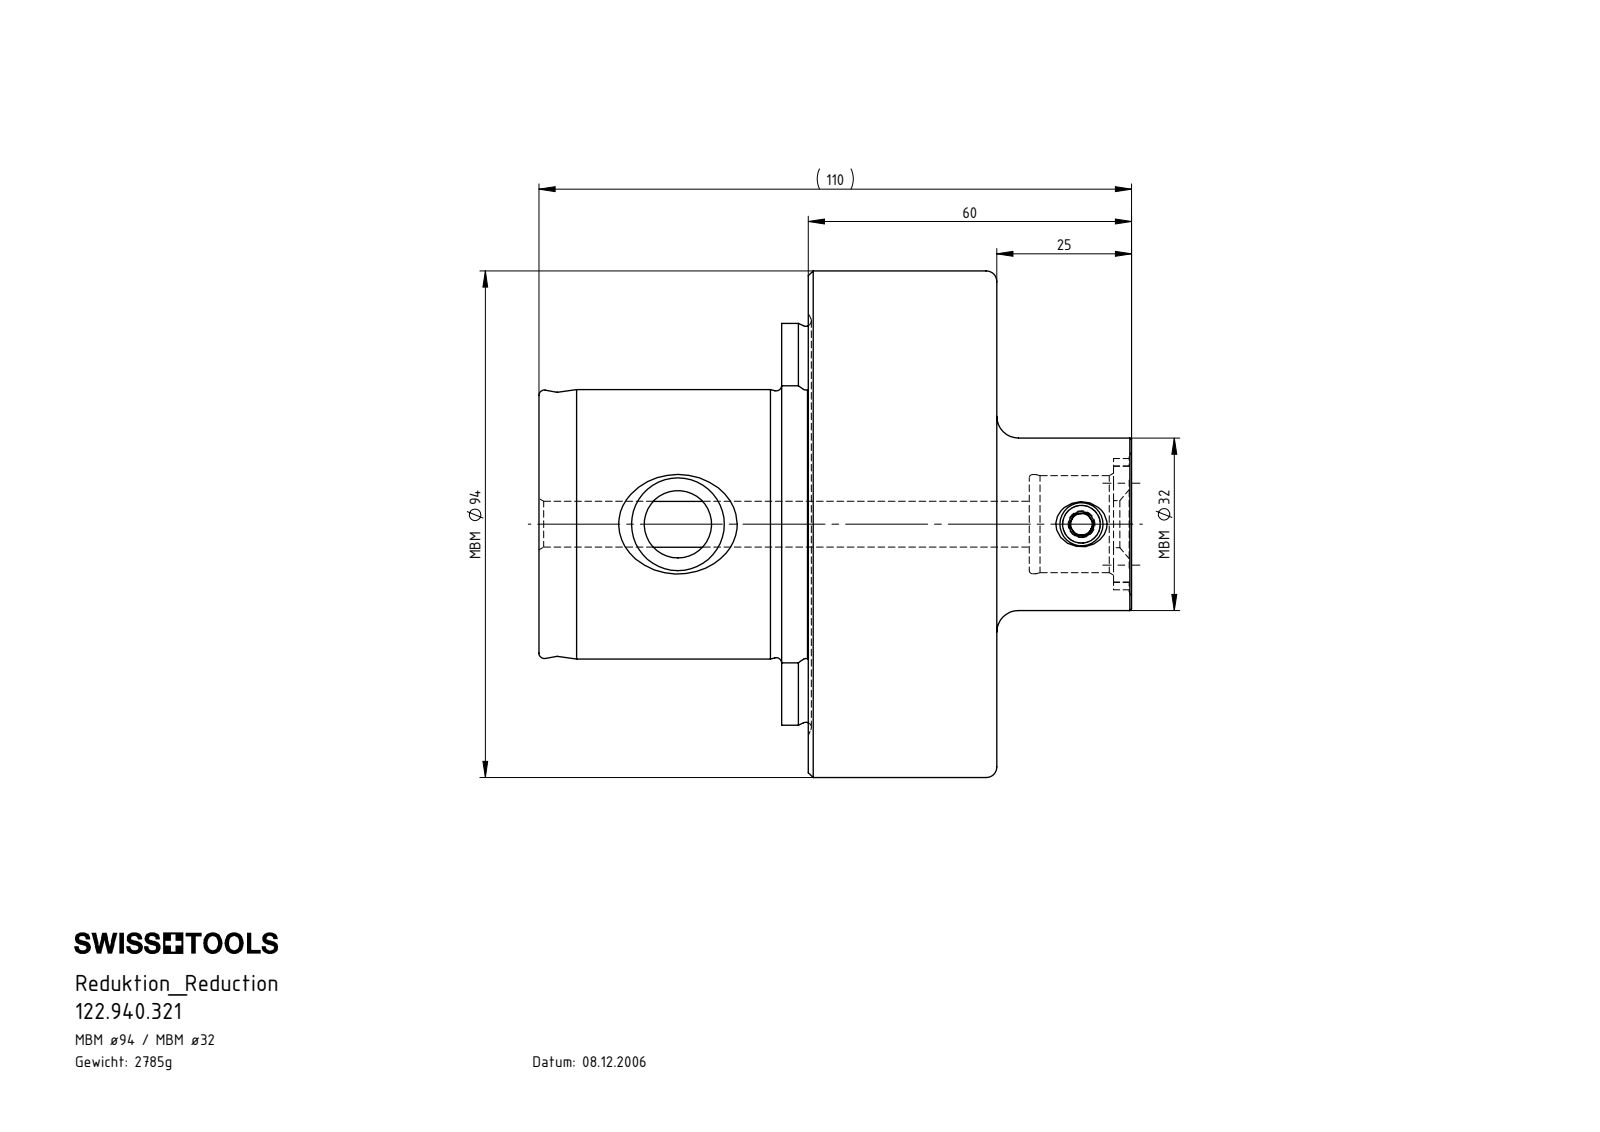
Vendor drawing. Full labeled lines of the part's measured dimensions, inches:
Part name (STEP PRODUCT): MB9-MB3.K01.060_C; MB3-ER1.001.011_A; 122.940.321
STEP written by: SolidWorks 2017 (CONFIG_CONTROL_DESIGN)
Units: inches
Bodies: 2 solids, 137 faces (35 planar, 35 cylindrical, 67 other)
Overall size (bounding box): 4.331 × 3.701 × 3.701
Volume: 21.65 in³ · Surface area: 60.1 in²
Round holes (diameter × count): ⌀0.157 ×1, ⌀0.276 ×1, ⌀0.335 ×1, ⌀0.492 ×1, ⌀0.709 ×1, ⌀0.724 ×1
Round bosses / shafts (diameter × count): ⌀3.701 ×1, ⌀1.969 ×1, ⌀1.26 ×1, ⌀0.315 ×1
Partial cylindrical surfaces — rounded edges, fillets, slot ends (radius × count): R0.126 ×4, R0.413 ×1, R0.48 ×1, R1.467 ×1
Main face-to-face distances: 1.378, 1.969, 3.346, 1.774, 0.195, 1.573, 1.963, 0.189, 1.384, 2.126
Hole centre spacings: 2.949
